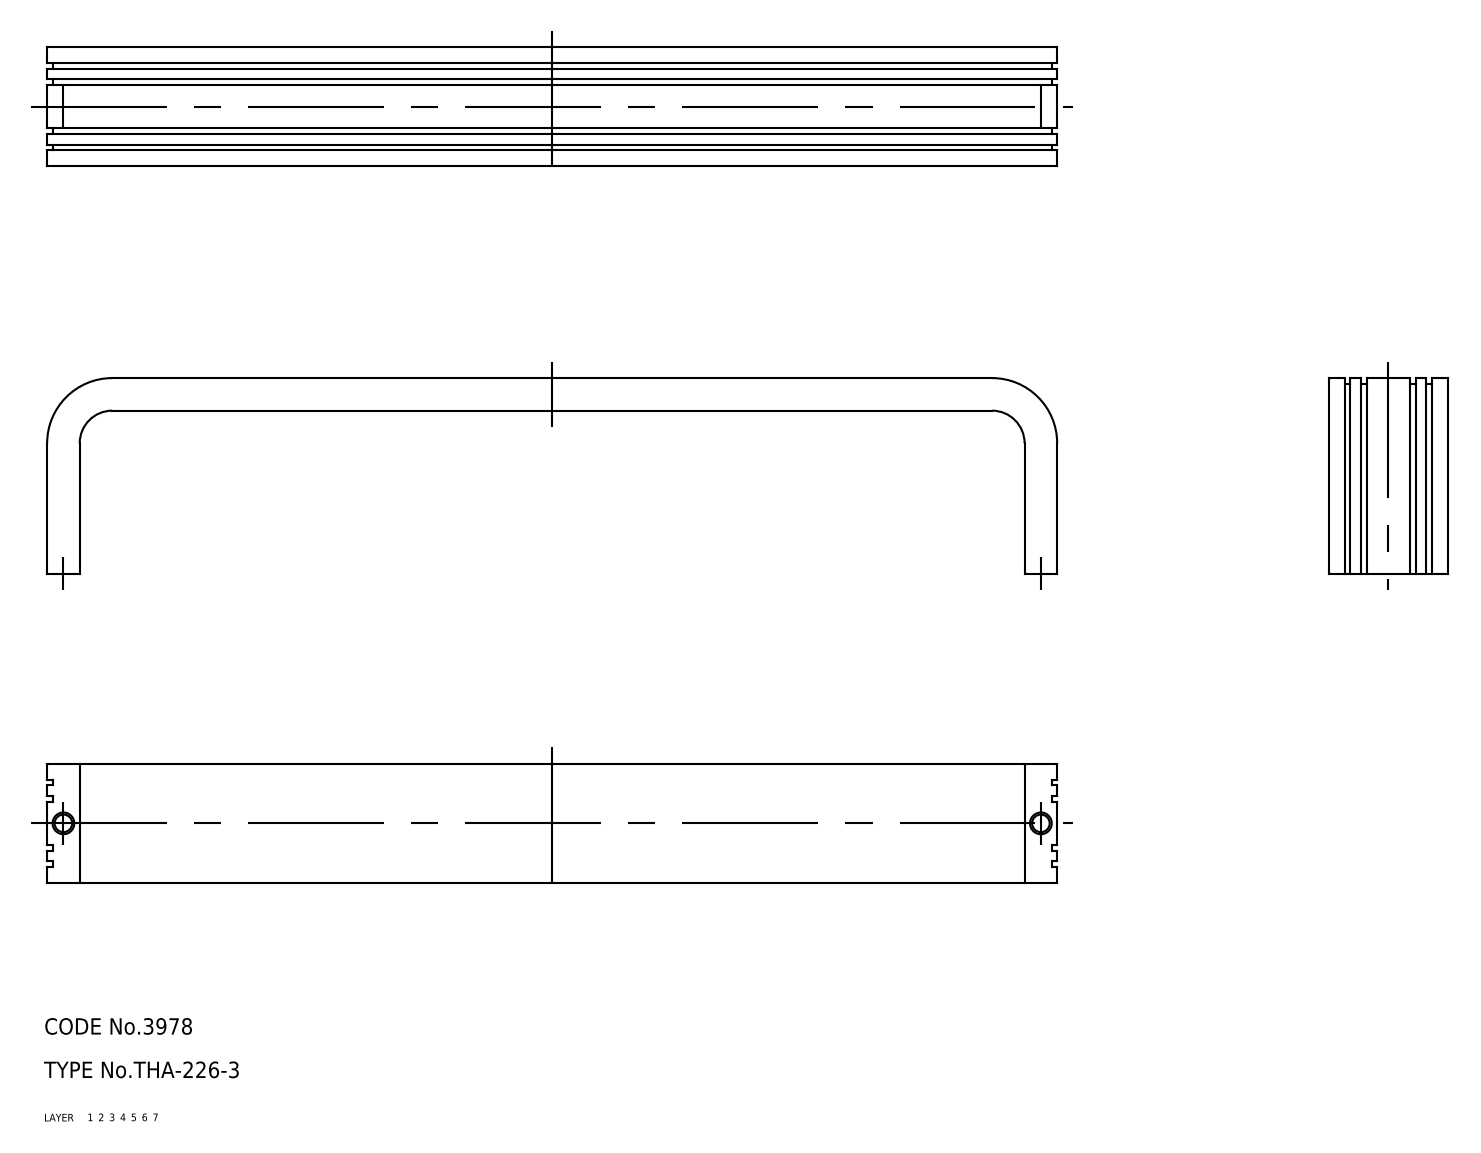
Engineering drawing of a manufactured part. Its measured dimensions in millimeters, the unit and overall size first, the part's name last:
Units: millimetres
Overall size (bounding box): 186 × 36 × 22
Volume: 30 317 mm³ · Surface area: 15 707 mm²
Bodies: 1 solid, 68 faces (0 planar, 0 cylindrical, 68 other)
Part name (STEP PRODUCT): pull
STEP written by: CADfix (AUTOMOTIVE_DESIGN)
